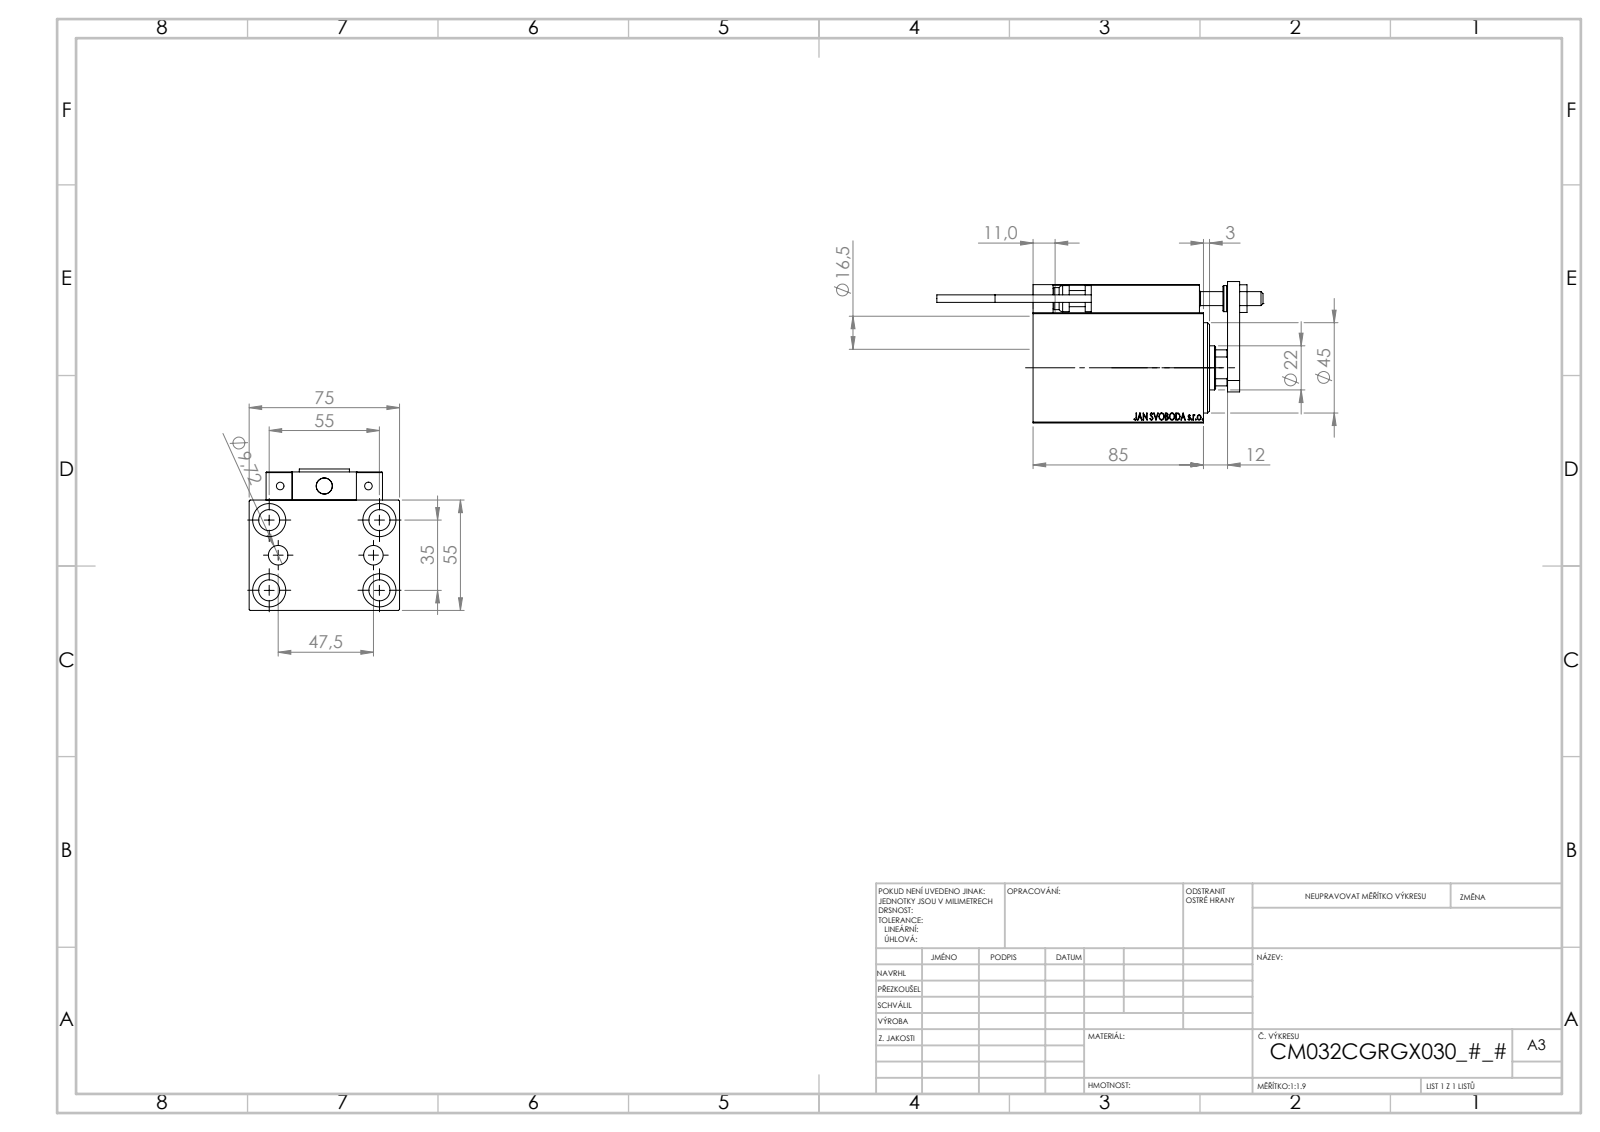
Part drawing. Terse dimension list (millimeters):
name: ALLEN BOLT D8; SWITCH_X_FRONT_BACK; ZARAZKA; ALLEN BOLT D5 (+7 more)
written by: SolidWorks 2019 (CONFIG_CONTROL_DESIGN)
unit: mm
bodies: 23 solids, 1278 faces (560 planar, 184 cylindrical, 534 other)
size: 162.7 × 75 × 70.5
volume: 347 795 mm³; area: 87 402 mm²
holes: 6× ⌀4, 5× ⌀8, 5× ⌀10.5, 5× ⌀16.5, 4× ⌀3.2, 2× ⌀5, 2× ⌀9.72, 1× ⌀7, 1× ⌀22, 1× ⌀25.5, 1× ⌀32, 1× ⌀34
bosses: 2× ⌀5, 2× ⌀3.8, 1× ⌀13, 1× ⌀11
rounds: 30× R0.3, 2× R3, 1× R10.5
face distances: 55, 75, 14, 69, 5, 25, 10, 18, 12, 3
hole spacings: 17.9, 32.6, 54.16, 11.37, 20, 23.75, 29.59, 29.69
